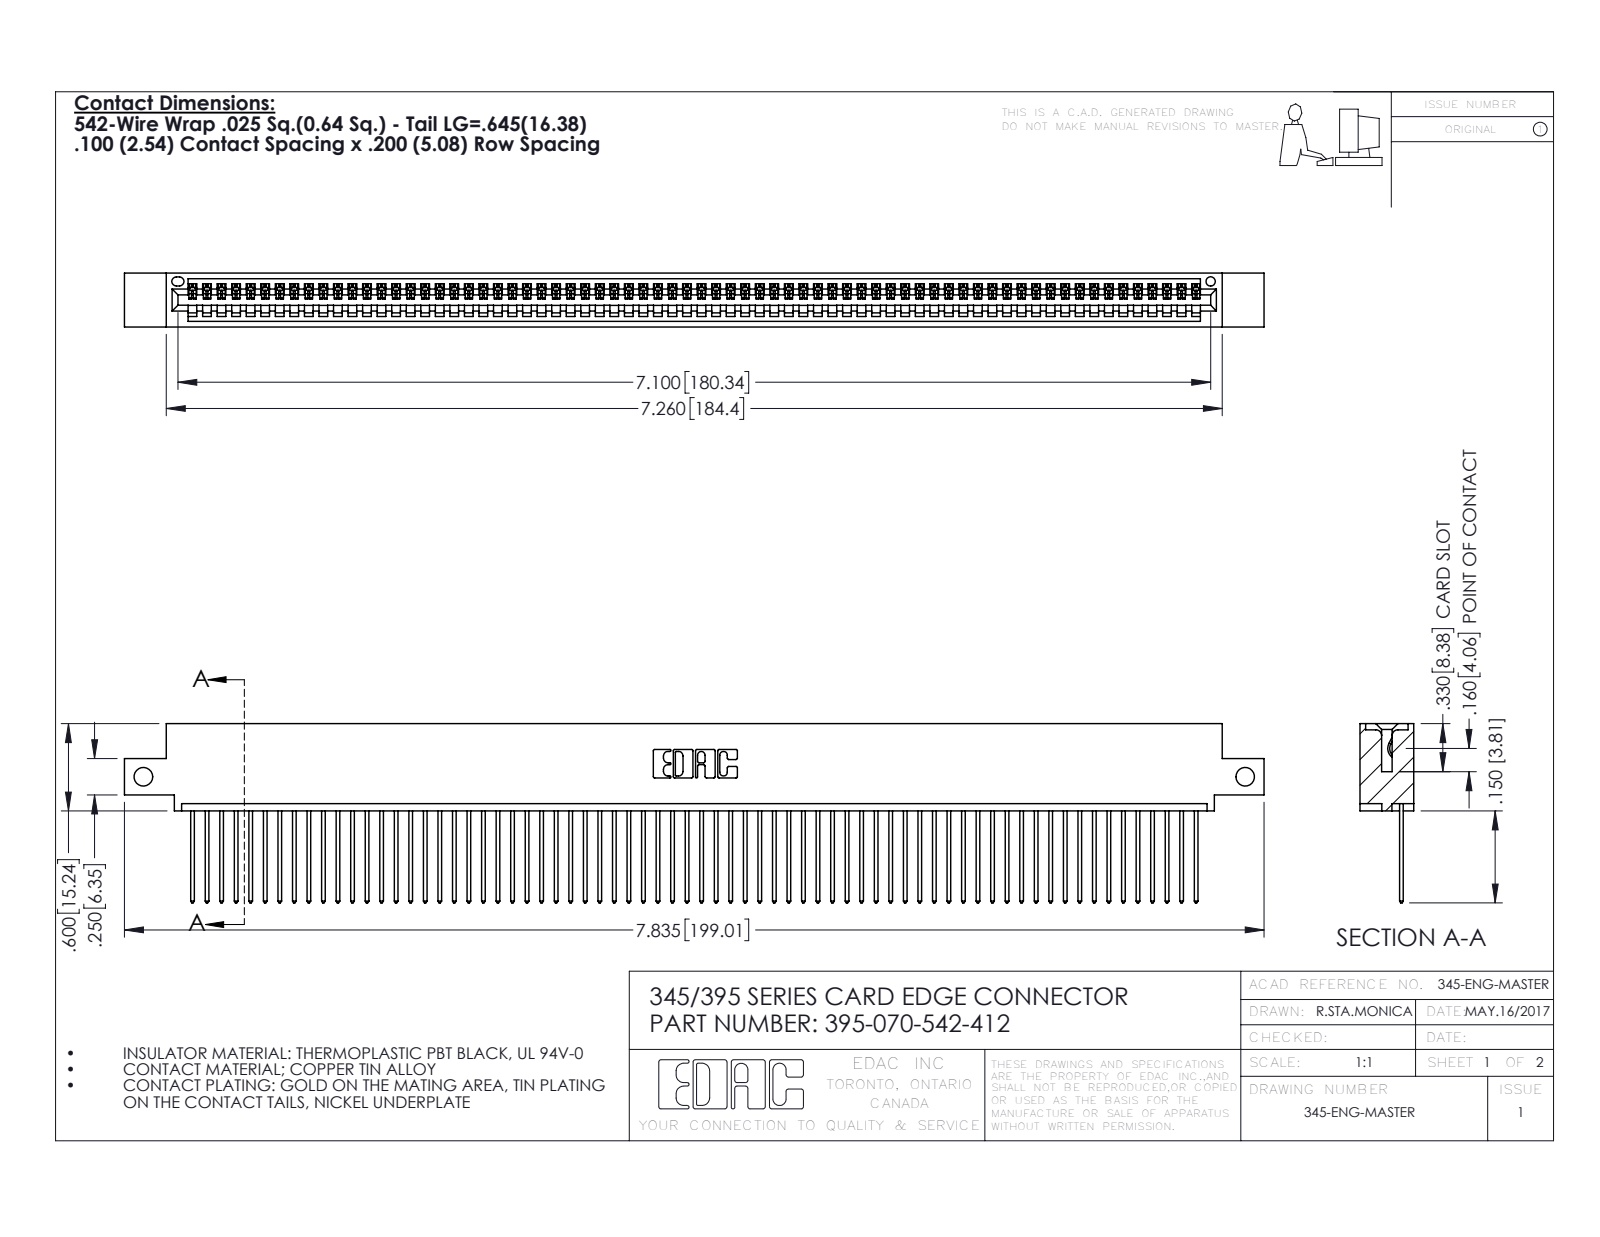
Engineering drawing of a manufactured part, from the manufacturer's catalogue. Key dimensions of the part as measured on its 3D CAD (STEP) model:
Part name (STEP PRODUCT): 395-070-542-412; 345-292-001_345-293-142; 345 Part_0.110 Offset - Side Mount
STEP written by: SolidWorks 2016 (CONFIG_CONTROL_DESIGN)
Units: inches
Bodies: 71 solids, 4190 faces (2884 planar, 1306 cylindrical, 0 other)
Overall size (bounding box): 7.835 × 1.232 × 0.37
Volume: 1.167 in³ · Surface area: 41.42 in²
Round holes (diameter × count): ⌀0.128 ×2, ⌀0.064 ×1
Partial cylindrical surfaces — rounded edges, fillets, slot ends (radius × count): R0.006 ×140, R0.01 ×140, R0.01 ×22, R0.007 ×6, R0.031 ×6, R0.026 ×3, R0.031 ×2, R0.04 ×2
Main face-to-face distances: 0.072, 0.298, 0.098, 0.272, 0.025, 0.37, 0.2, 0.225, 0.149, 0.072
Hole centre spacings: 7.575
